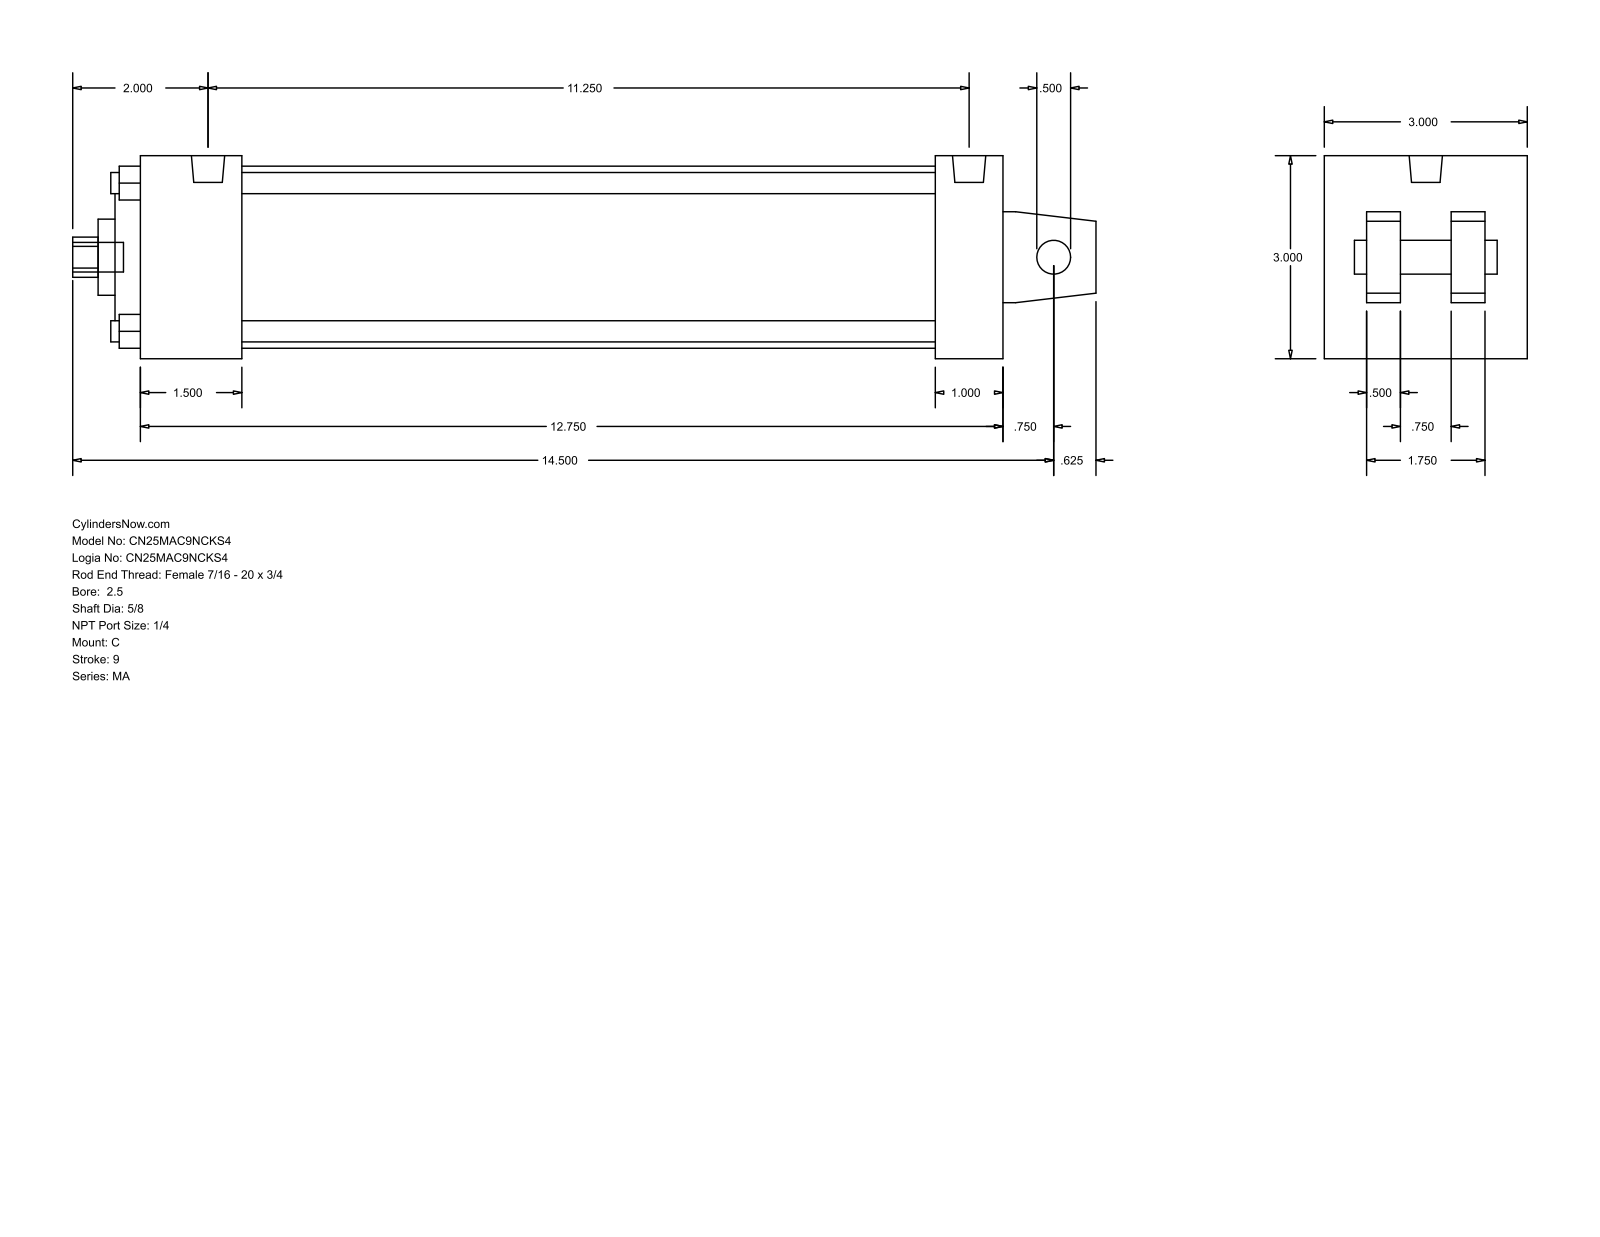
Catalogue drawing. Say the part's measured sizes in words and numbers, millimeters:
The part is named "MA_C__0250_0.625". Its 3-D file was written by "GSSL Pune (CONFIG_CONTROL_DESIGN)". It is 0 solids with 105 faces: 77 planar, 28 cylindrical and 0 other. Overall it measures 384.18 by 76.2 by 76.2 millimeters. Round holes: 4 of diameter 7.94, 1 of diameter 12.7, 1 of diameter 15.88, 1 of diameter 28.57, 1 of diameter 50.8, 1 of diameter 68.33. Round bosses or shafts: 4 of diameter 7.94, 2 of diameter 12.49, 1 of diameter 11.11. Partial cylindrical surfaces (rounded edges, fillets, slot ends): 1 of radius 7.54. The main face-to-face distances are 76.2, 323.85, 12.7, 15.87, 60.33, 47.63, 25.4, 38.1, 298.45, 260.35. The hole center spacings are 39.33, 55.62, 78.66.
